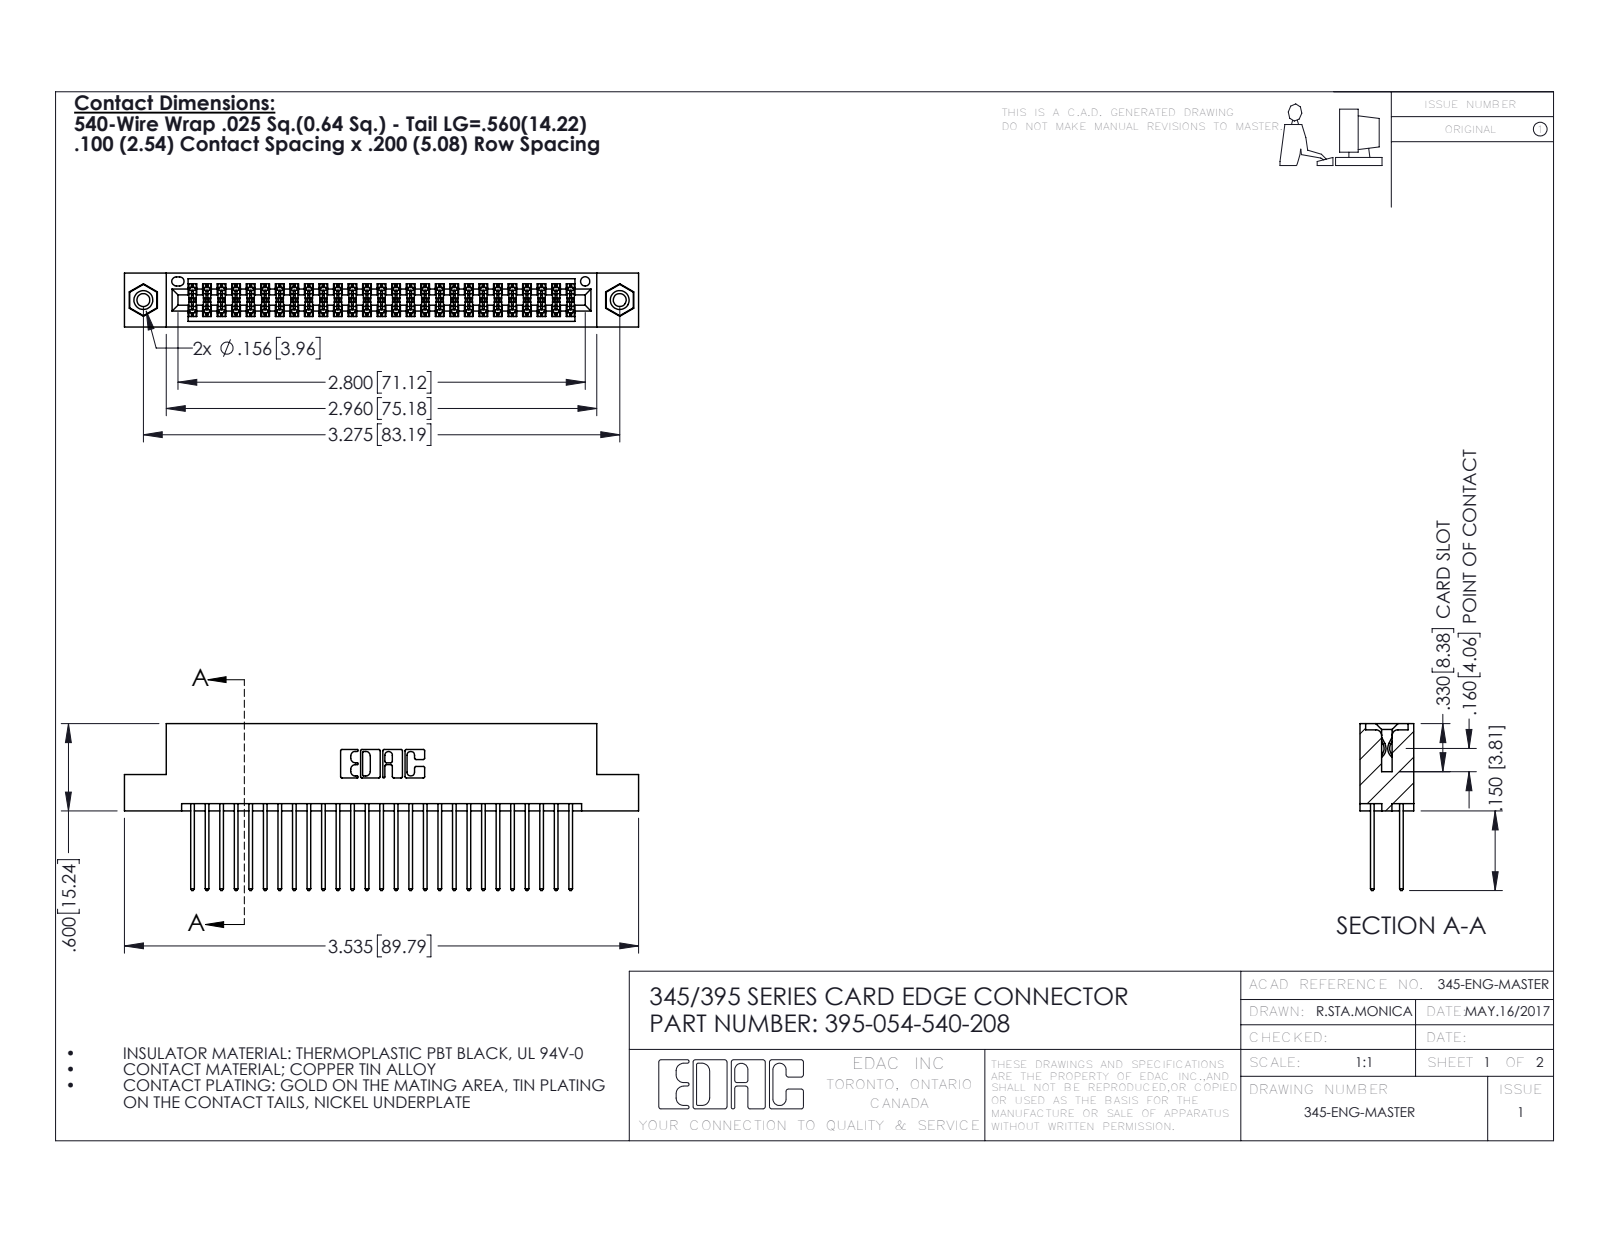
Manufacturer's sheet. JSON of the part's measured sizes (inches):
{"part_name": "345 Part_Flush Mounting Lugs - 0.156 Dia-TI; 395-054-540-208; 345-250-001_345-250-003-102; 345-292-001_345-293-140", "step_written_by": "SolidWorks 2016 (CONFIG_CONTROL_DESIGN)", "units": "inches", "bodies": {"solids": 57, "faces": 2886, "planar": 1894, "cylindrical": 976, "other": 16}, "overall_size": [3.535, 1.147, 0.37], "volume_in3": 0.536, "surface_area_in2": 21.16, "round_holes": [[0.089, 2], [0.125, 2], [0.156, 2], [0.064, 1]], "round_bosses_or_shafts": [[0.155, 2]], "partial_cylinders_radius": [[0.006, 81], [0.01, 54], [0.01, 22], [0.007, 6], [0.031, 6], [0.026, 3], [0.014, 2], [0.019, 2]], "face_to_face_distances": [0.072, 0.298, 0.2, 0.098, 0.272, 0.025, 0.37, 0.225, 0.175, 0.149], "hole_center_spacings": [0.27, 3.04, 3.275]}
